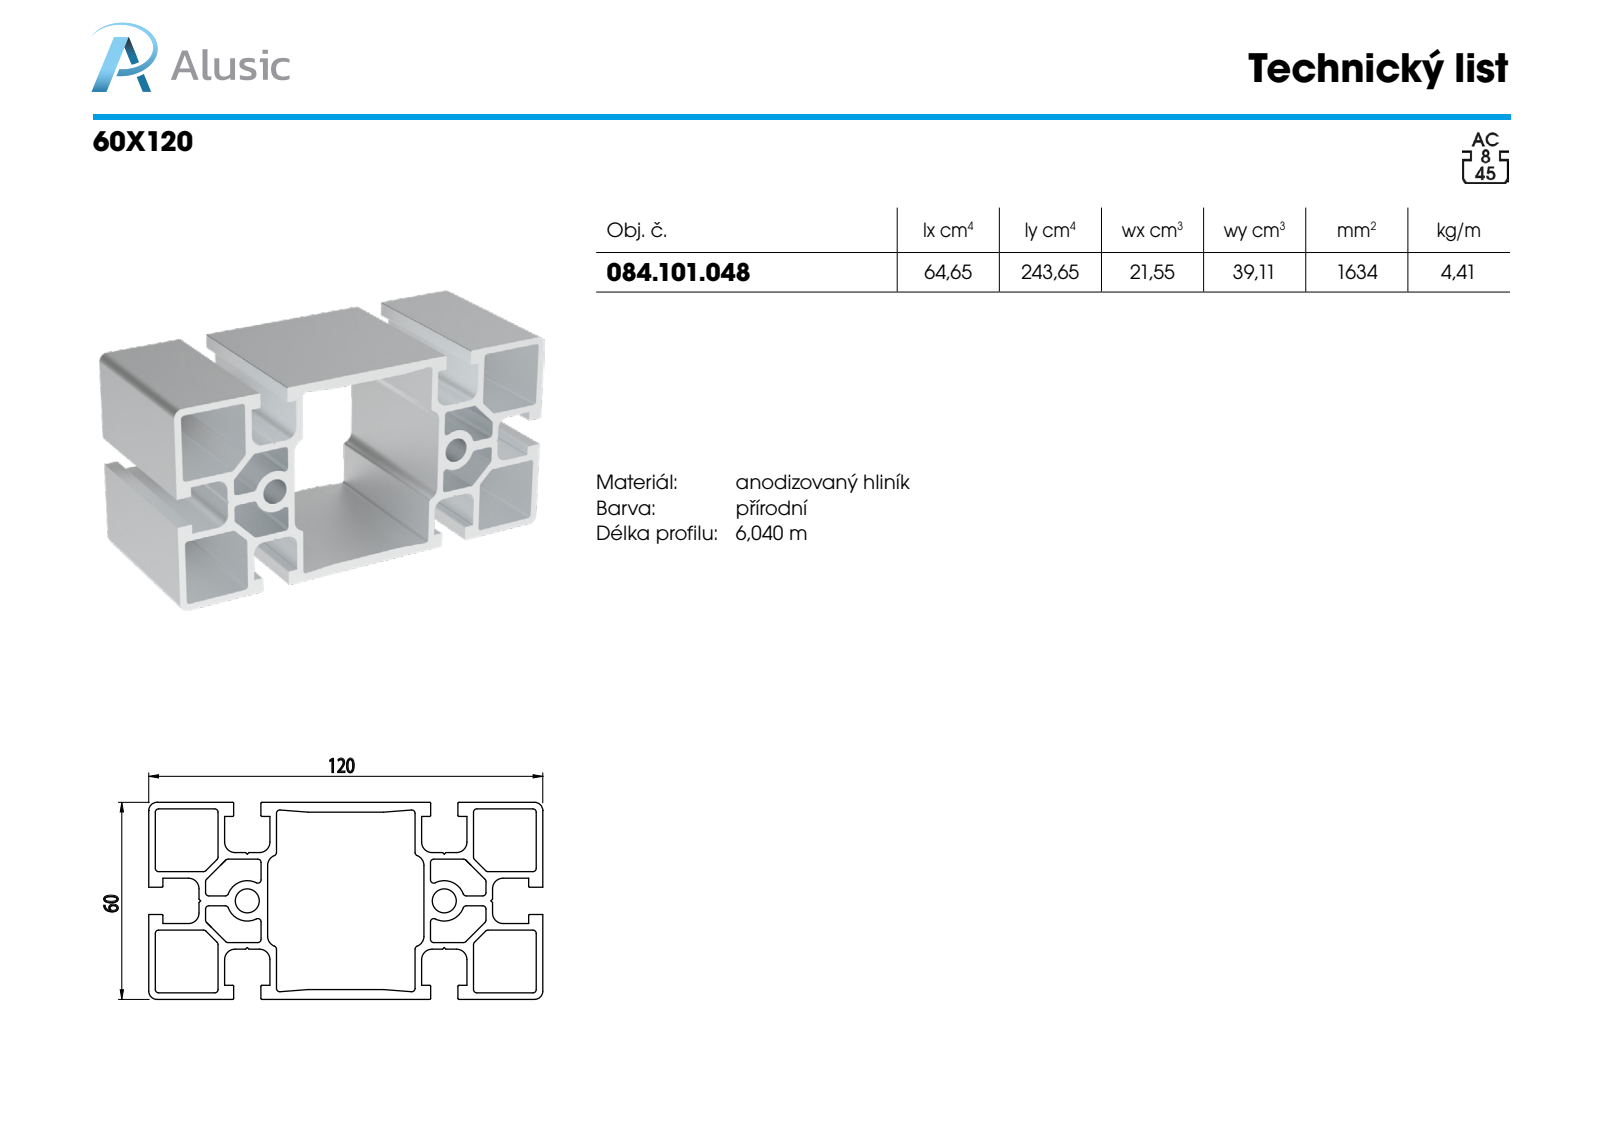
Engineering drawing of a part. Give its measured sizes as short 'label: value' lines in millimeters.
name: 084.101.048
written by: SolidWorks 2018 (AUTOMOTIVE_DESIGN)
unit: mm
bodies: 1 solid, 230 faces (124 planar, 106 cylindrical, 0 other)
size: 120 × 100 × 60
volume: 163 370 mm³; area: 135 309 mm²
holes: 2× ⌀7.3
rounds: 52× R1, 18× R0.3, 16× R3.2, 4× R2.5, 2× R0.25, 2× R6.15
face distances: 2, 60, 21.1, 36.9, 19.1, 38.9, 58, 15.8, 96.9, 81.1
hole spacings: 60
